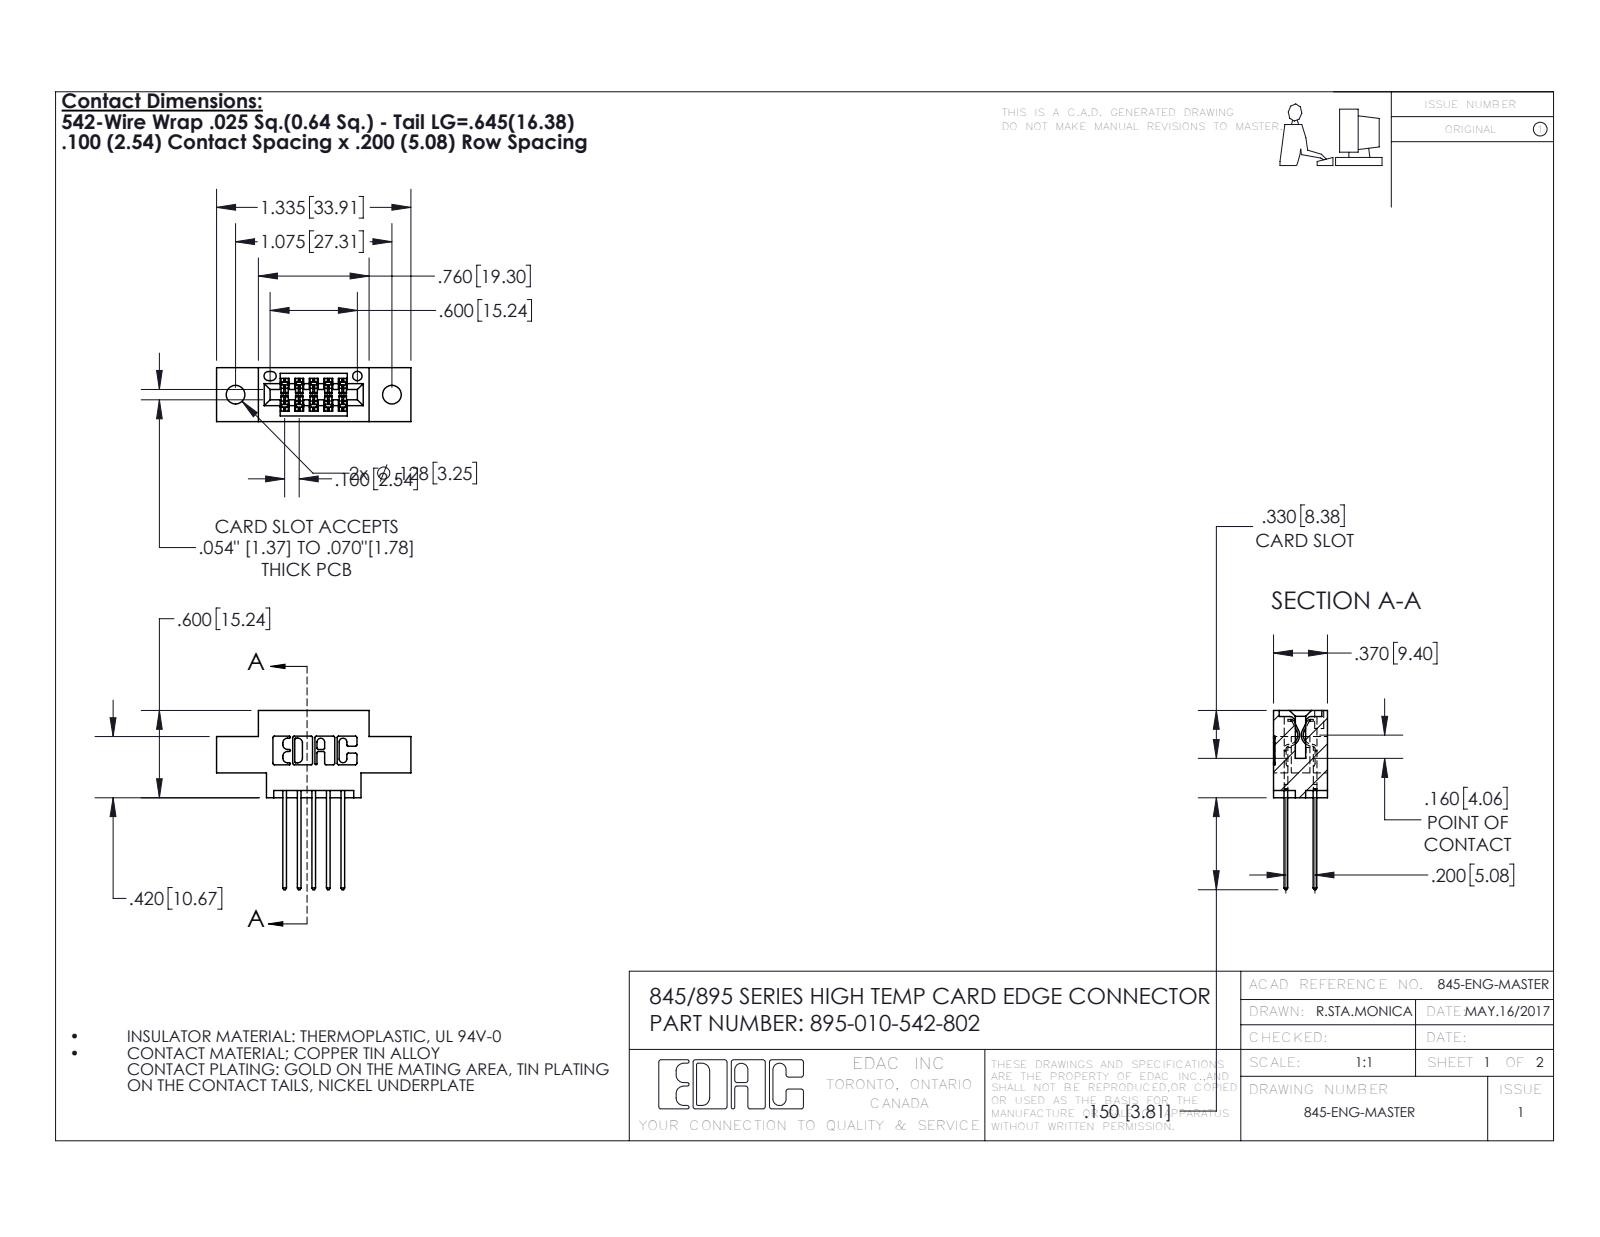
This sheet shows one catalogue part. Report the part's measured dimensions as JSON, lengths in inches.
{"part_name": "345-292-001_345-293-142; 395-010-542-802; 345 Part_0.170 Offset - 0.128 Dia", "step_written_by": "SolidWorks 2016 (CONFIG_CONTROL_DESIGN)", "units": "inches", "bodies": {"solids": 11, "faces": 630, "planar": 414, "cylindrical": 216, "other": 0}, "overall_size": [1.335, 1.232, 0.37], "volume_in3": 0.174, "surface_area_in2": 5.55, "round_holes": [[0.128, 2], [0.064, 1]], "partial_cylinders_radius": [[0.01, 22], [0.006, 15], [0.01, 10], [0.007, 6], [0.031, 6], [0.026, 3], [0.014, 2], [0.019, 2]], "face_to_face_distances": [0.2, 0.37, 0.072, 0.298, 0.1, 0.098, 0.272, 0.025, 0.225, 0.25], "hole_center_spacings": [0.27, 0.847, 1.075]}
